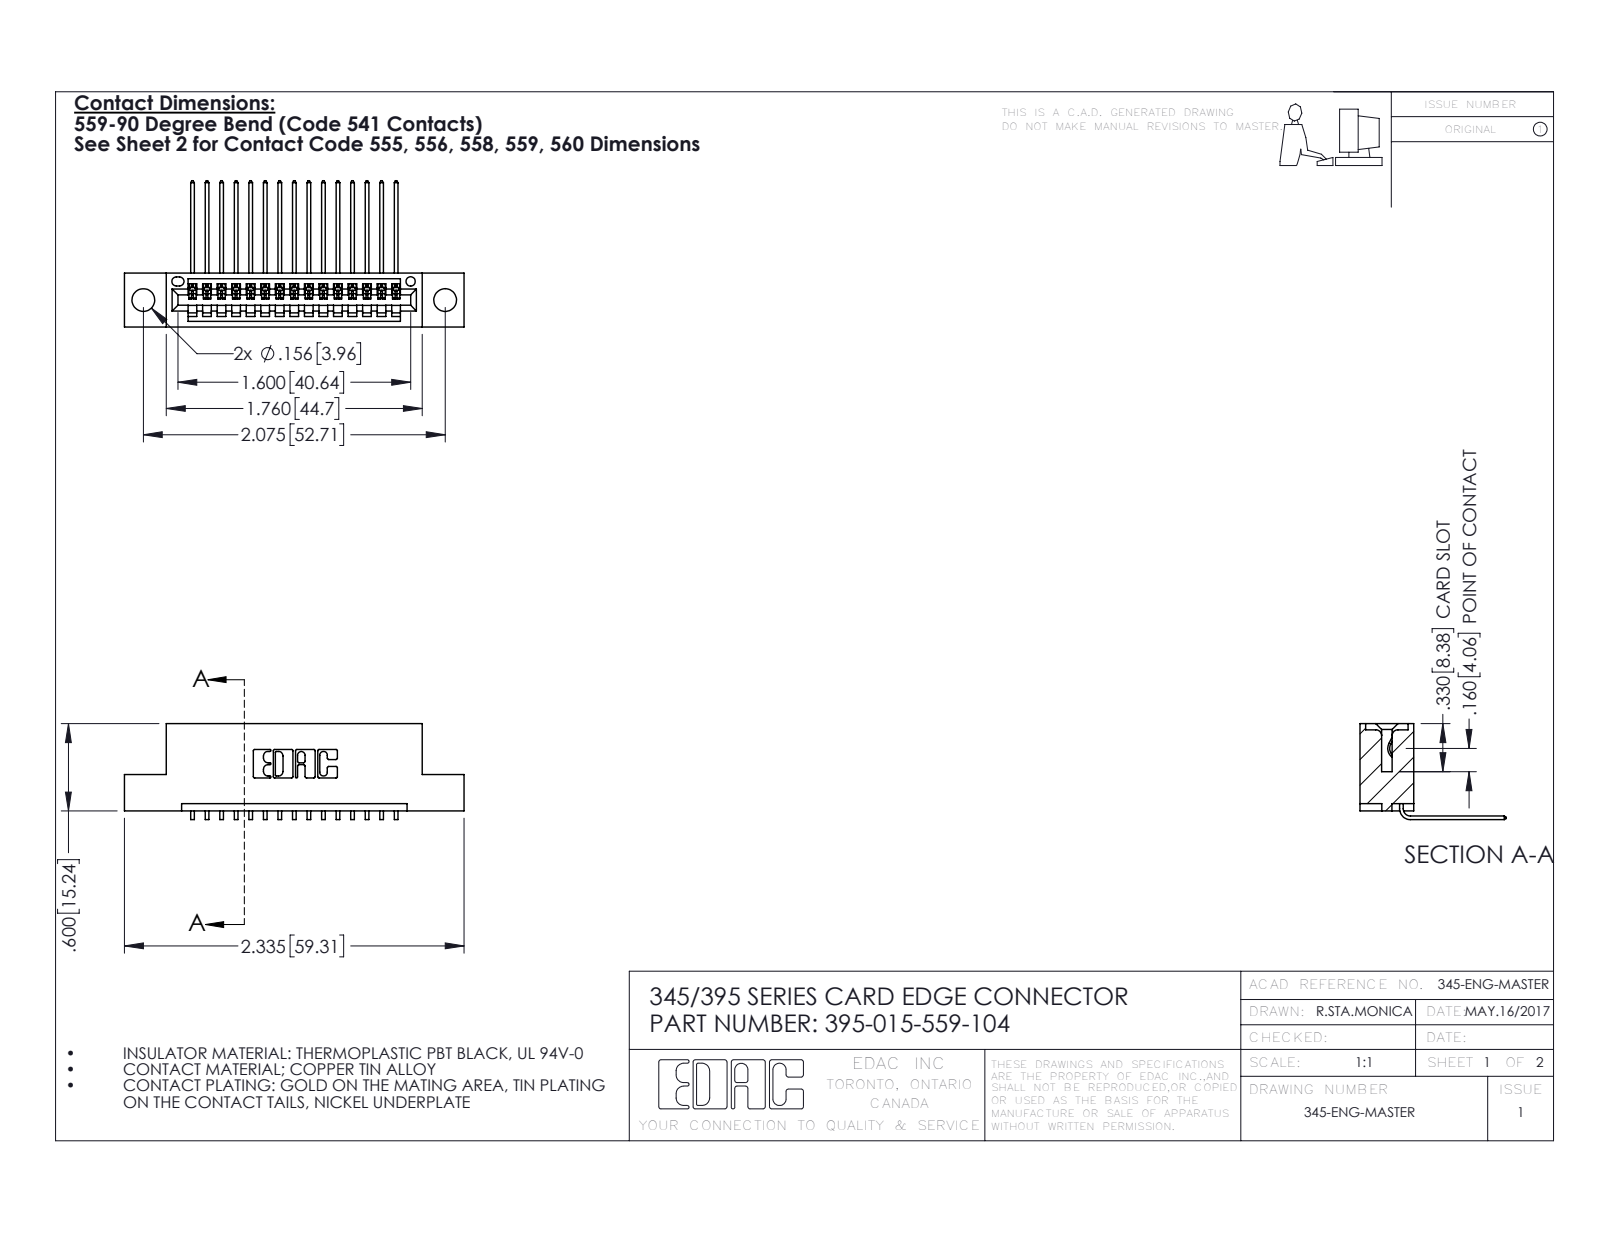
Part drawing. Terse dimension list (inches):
name: 345-292-001_558 559 Tail - 1; 395-015-559-104; 345 Part_Flush Mounting Lugs - 0.156 Dia-TH
written by: SolidWorks 2016 (CONFIG_CONTROL_DESIGN)
unit: in
bodies: 16 solids, 1026 faces (710 planar, 316 cylindrical, 0 other)
size: 2.335 × 1.005 × 0.659
volume: 0.328 in³; area: 10.66 in²
holes: 2× ⌀0.156, 1× ⌀0.064
rounds: 30× R0.006, 22× R0.01, 6× R0.007, 6× R0.031, 3× R0.026, 2× R0.031, 2× R0.04, 1× R0.014
face distances: 0.2, 0.298, 0.072, 0.37, 0.098, 0.272, 0.025, 0.1, 0.225, 0.05
hole spacings: 0.27, 1.842, 2.075
